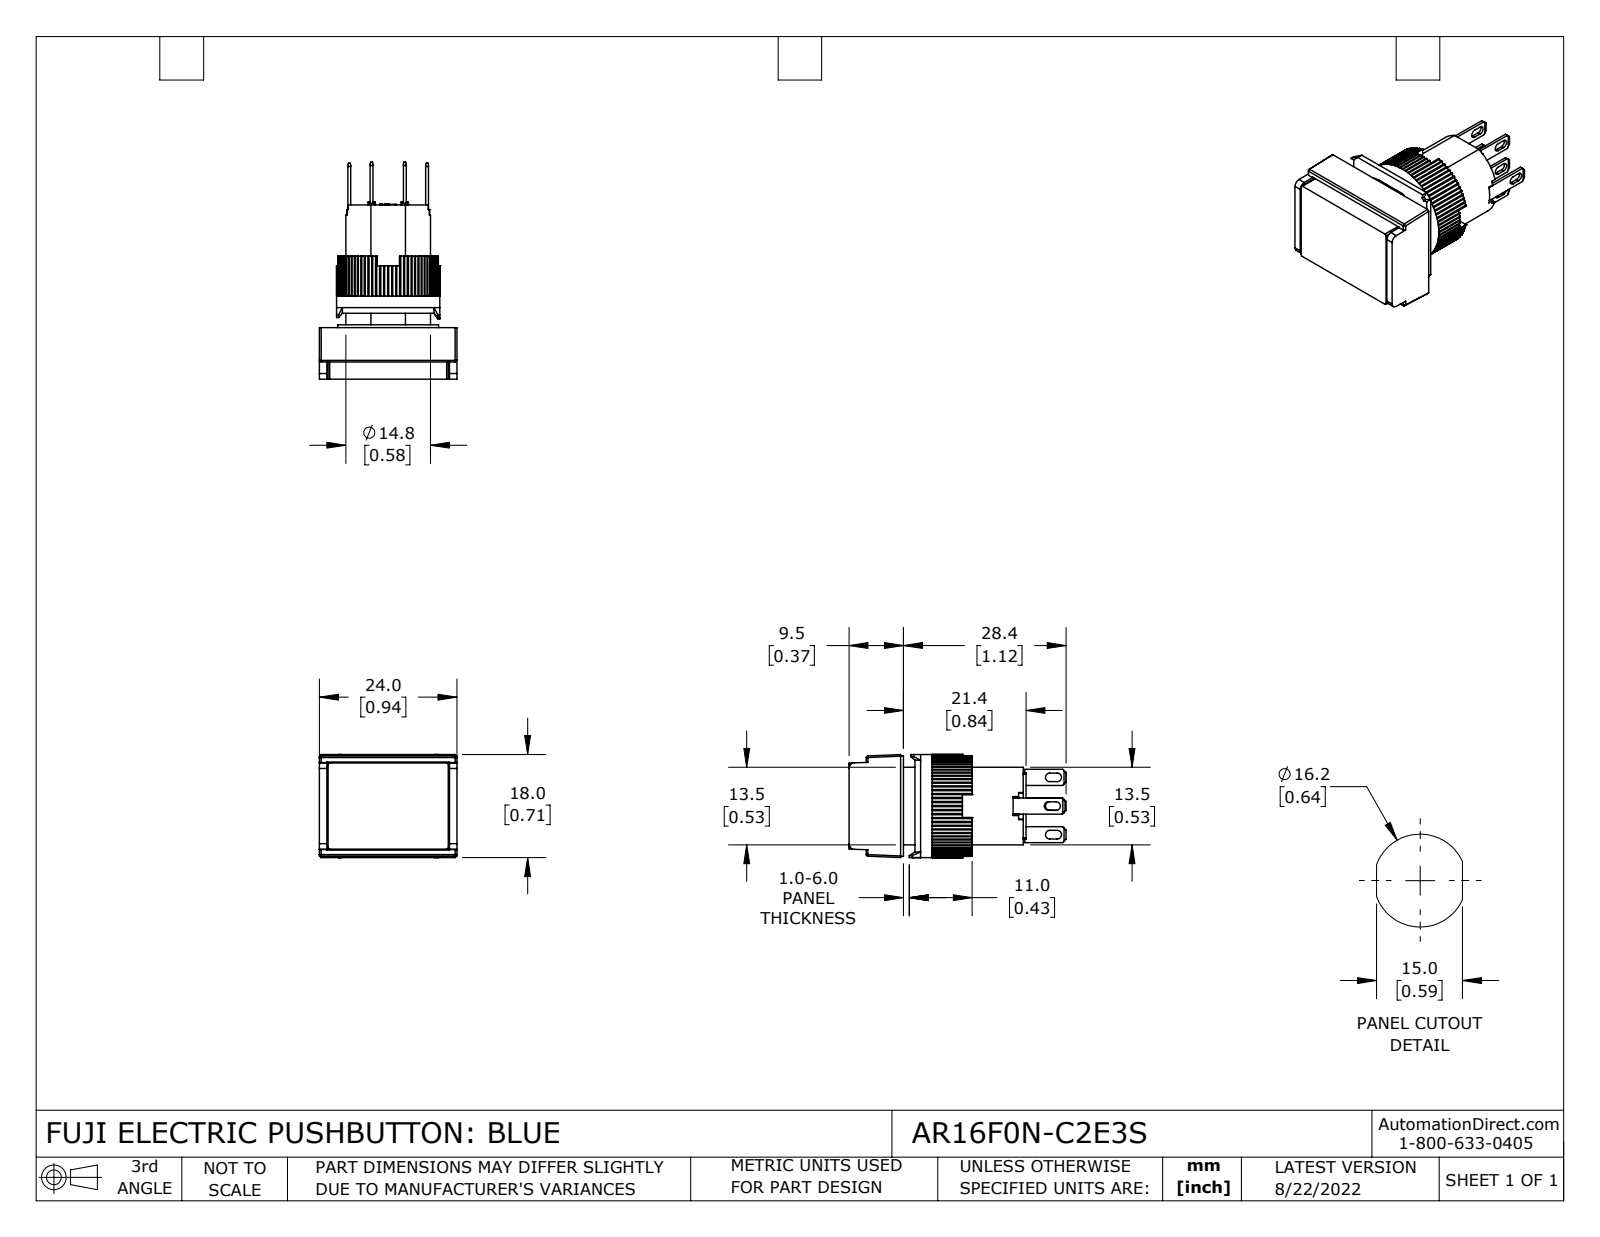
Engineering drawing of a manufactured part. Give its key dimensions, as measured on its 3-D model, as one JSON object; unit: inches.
{"part_name": "AR16F0N-C2E3S", "step_written_by": "SolidWorks 2023 (CONFIG_CONTROL_DESIGN)", "units": "inches", "bodies": {"solids": 14, "faces": 845, "planar": 656, "cylindrical": 185, "other": 4}, "overall_size": [1.492, 0.945, 0.709], "volume_in3": 0.469, "surface_area_in2": 9.459, "round_holes": [[0.543, 1], [0.583, 1]], "round_bosses_or_shafts": [[0.709, 1], [0.693, 1]], "partial_cylinders_radius": [[0.01, 80], [0.008, 12], [0.03, 8], [0.012, 6], [0.039, 2], [0.315, 1]], "face_to_face_distances": [0.213, 0.354, 0.142, 0.35, 0.492, 0.705, 0.138, 0.02, 0.843, 0.764]}
